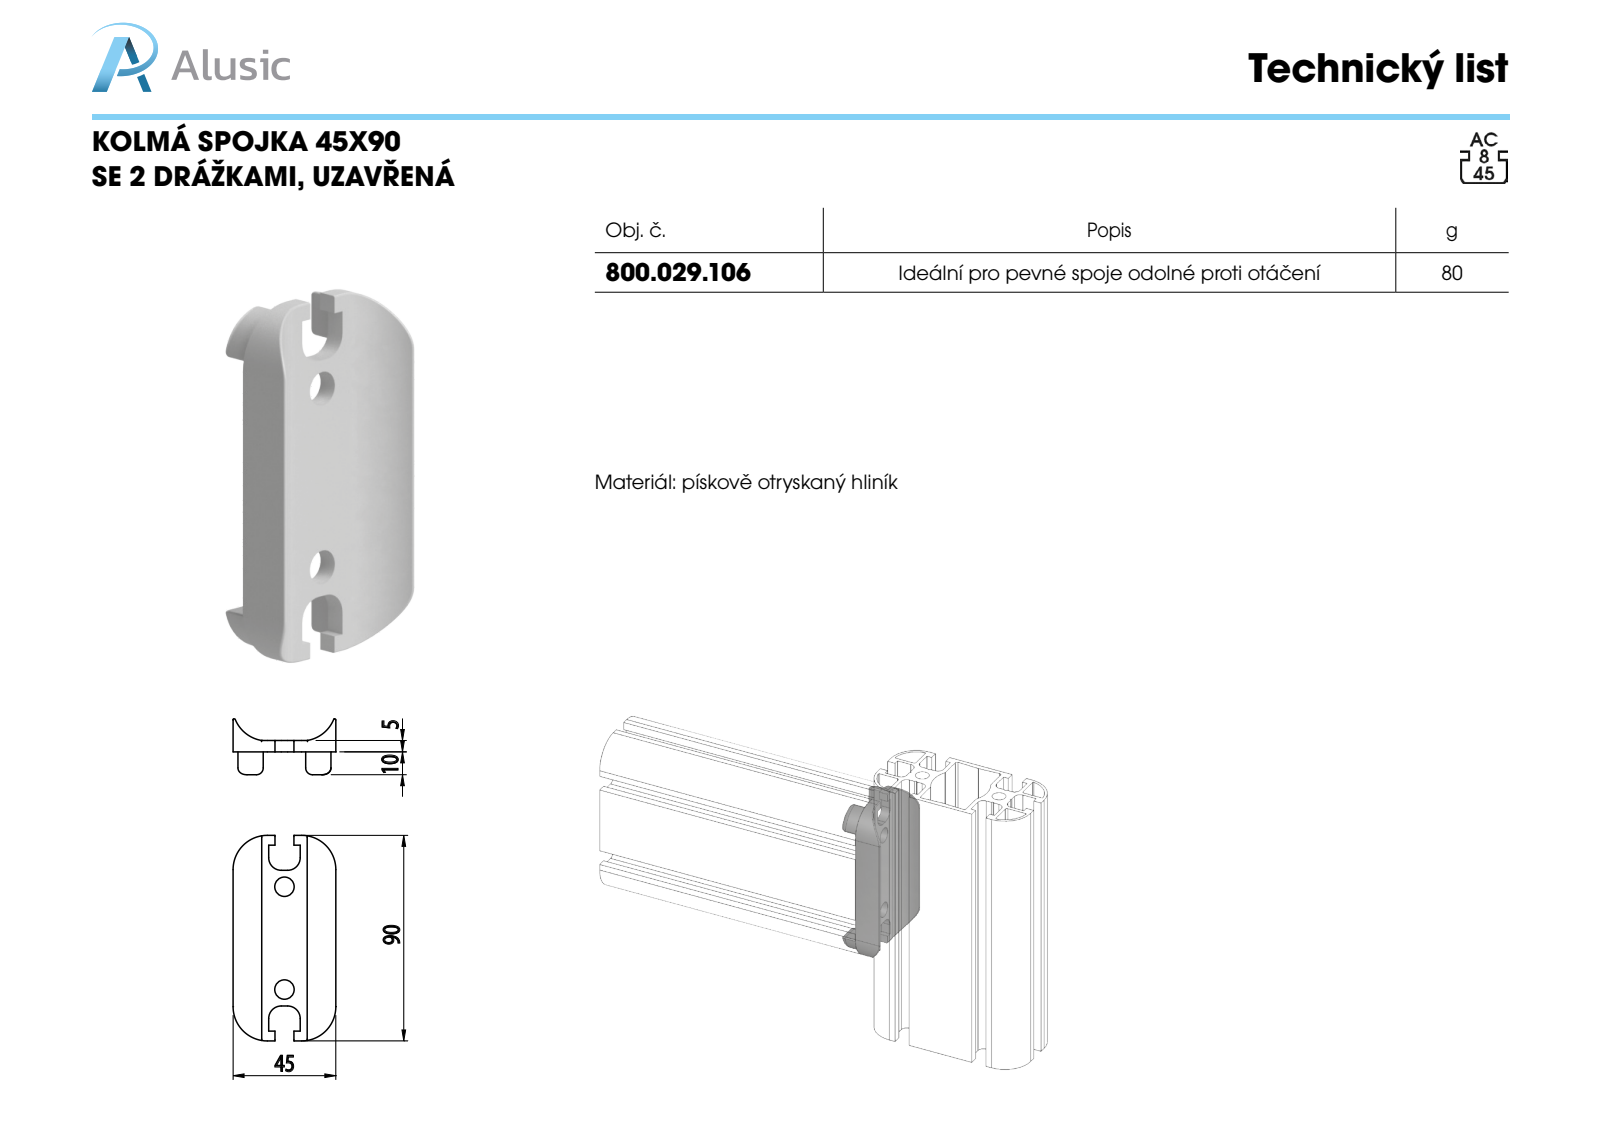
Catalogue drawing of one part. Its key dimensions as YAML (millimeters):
part_name: "800.029.106-2"
step_written_by: "SolidWorks 2011 (CONFIG_CONTROL_DESIGN)"
units: millimeters
bodies: {solids: 1, faces: 104, planar: 34, cylindrical: 46, other: 24}
overall_size: [90, 45, 24.48]
volume: 26912
surface_area: 12038
round_holes:
  - {diameter: 8.5, count: 2}
partial_cylinders:
  - {radius: 0.6, count: 12}
  - {radius: 0.5, count: 4}
  - {radius: 3, count: 4}
  - {radius: 5.5, count: 4}
  - {radius: 13.1, count: 4}
  - {radius: 15, count: 4}
  - {radius: 15.2, count: 2}
face_to_face_distances: [5, 45, 13.2, 31.8, 18.6, 63.6, 15.6, 29.4, 2.4, 16.2]
hole_center_spacings: [45]
